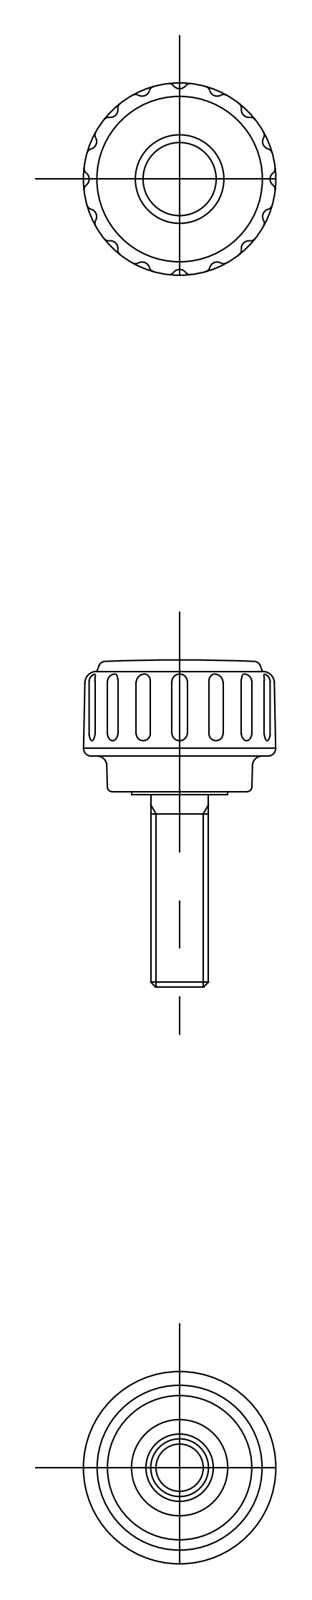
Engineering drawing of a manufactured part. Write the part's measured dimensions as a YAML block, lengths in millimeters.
part_name: "screw; knob; KDM_20_M6_20_23132_36"
step_written_by: "CADfix (AUTOMOTIVE_DESIGN)"
units: millimeters
bodies: {solids: 2, faces: 68, planar: 0, cylindrical: 0, other: 68}
overall_size: [33.95, 20.12, 19.97]
volume: 4090
surface_area: 2062
